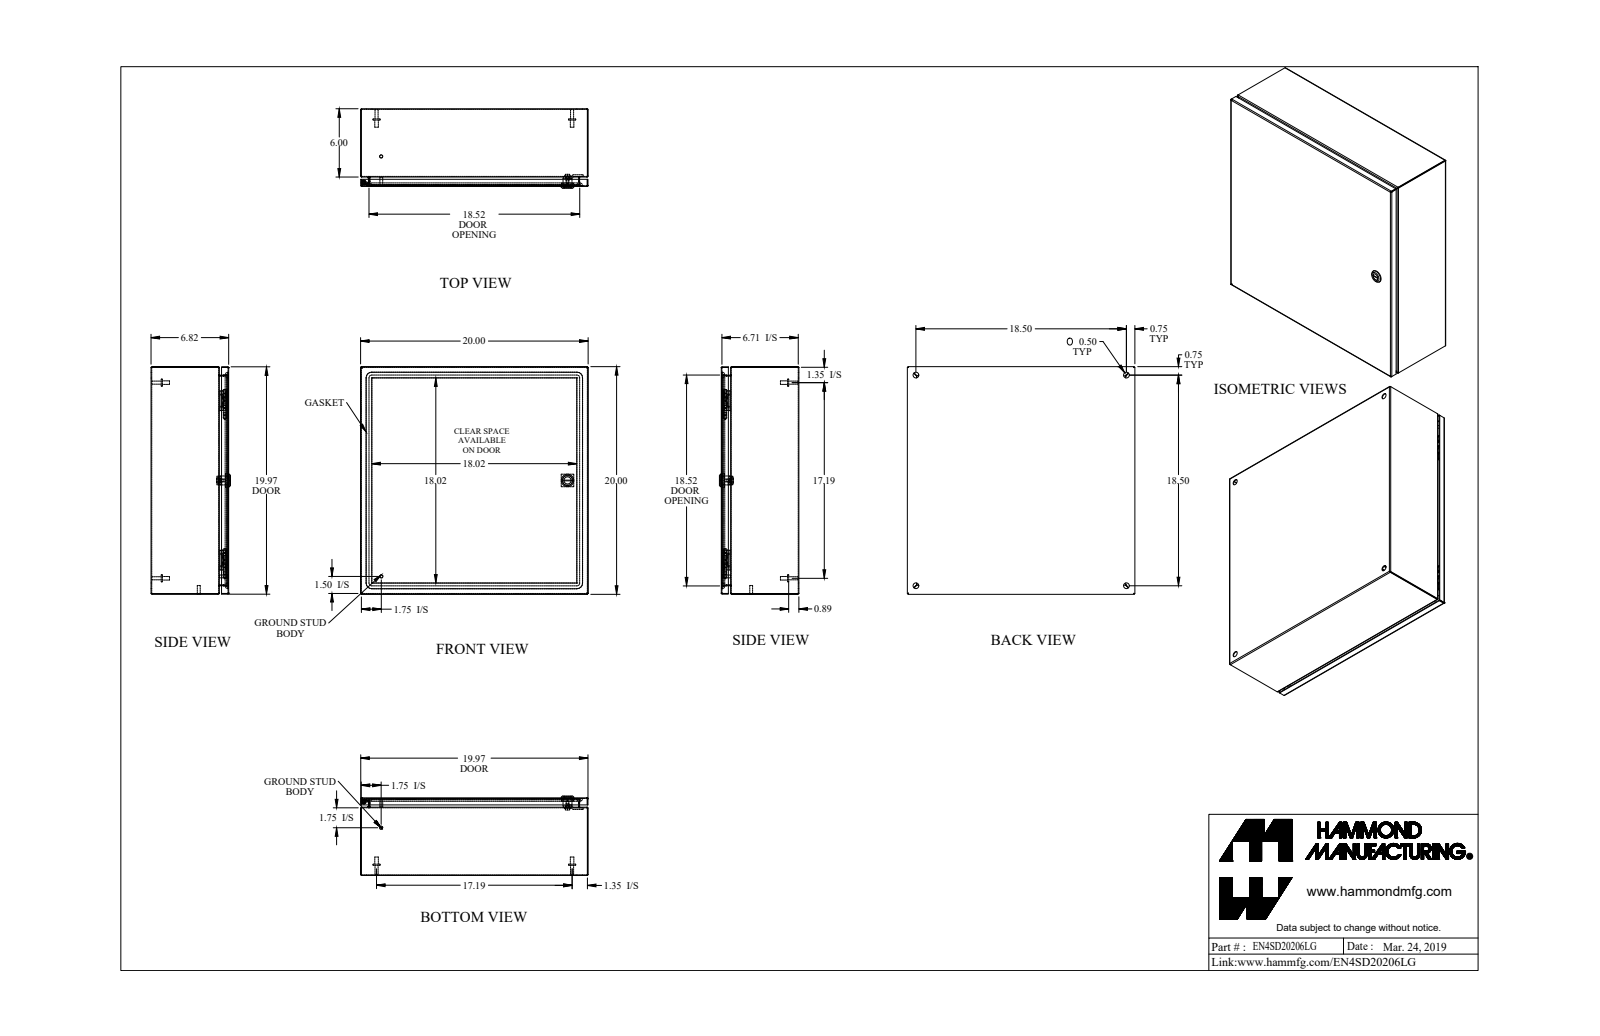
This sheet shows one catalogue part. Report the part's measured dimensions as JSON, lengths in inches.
{"part_name": "EN4SD20206LG_Default", "step_written_by": "SolidWorks 2019 (CONFIG_CONTROL_DESIGN)", "units": "inches", "bodies": {"solids": 21, "faces": 634, "planar": 285, "cylindrical": 213, "other": 136}, "overall_size": [20, 20, 6.982], "volume_in3": 89.75, "surface_area_in2": 3049, "round_holes": [[0.5, 4], [0.172, 1], [0.232, 1], [0.24, 1], [0.242, 1], [0.625, 1], [0.785, 1]], "round_bosses_or_shafts": [[0.625, 4], [0.313, 4], [0.27, 4], [0.281, 2], [0.25, 2], [1.1, 1], [0.525, 1], [0.455, 1]], "partial_cylinders_radius": [[0.029, 21], [0.086, 21], [0.25, 16], [19, 8], [0.006, 4], [0.062, 4], [0.499, 4], [0.125, 2]], "face_to_face_distances": [0.057, 6.765, 19.943, 6.708, 6.822, 19.886, 20, 0.822, 5.943, 0.749], "hole_center_spacings": [18.5, 26.163, 9.31, 9.311, 19.742, 19.742]}
